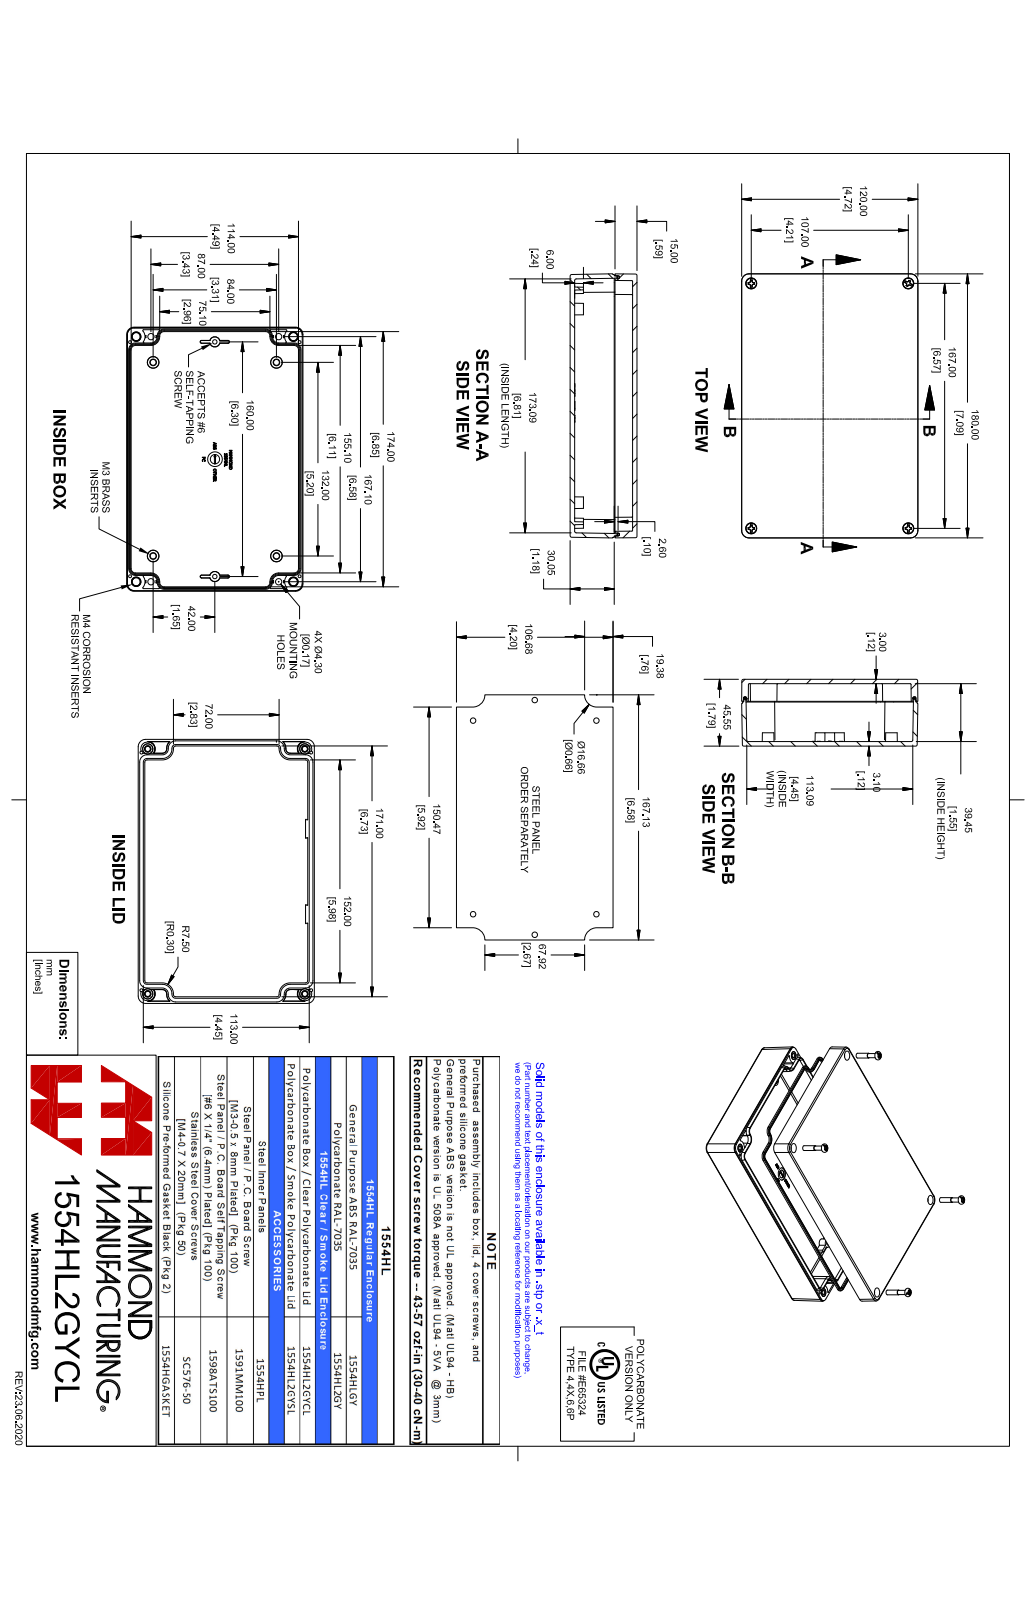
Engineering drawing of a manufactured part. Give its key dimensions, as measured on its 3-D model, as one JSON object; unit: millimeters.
{"part_name": "1554HL2GYCL", "step_written_by": "SolidWorks 2021 (AUTOMOTIVE_DESIGN)", "units": "millimeters", "bodies": {"solids": 15, "faces": 1478, "planar": 374, "cylindrical": 340, "other": 764}, "overall_size": [180.1, 120.1, 45.5], "volume_mm3": 220600, "surface_area_mm2": 156300, "round_holes": [[2, 4], [2.5, 4], [3.3, 4], [3.5, 4], [4.6, 4], [7, 4]], "round_bosses_or_shafts": [[6.4, 4], [5.5, 4], [5.3, 4], [4.8, 4], [3.9, 4], [3.9, 4], [3.8, 4], [3.4, 4]], "partial_cylinders_radius": [[0.5, 36], [1, 18], [5, 8], [0.8, 4], [3, 4], [4.7, 4]], "face_to_face_distances": [45.5, 3, 3.1, 42.4, 42.5, 39.4, 3, 4.5, 1.5, 12], "hole_center_spacings": [5, 20.9, 21.8, 97.1, 100.9, 111.4, 147.9, 149.9]}
